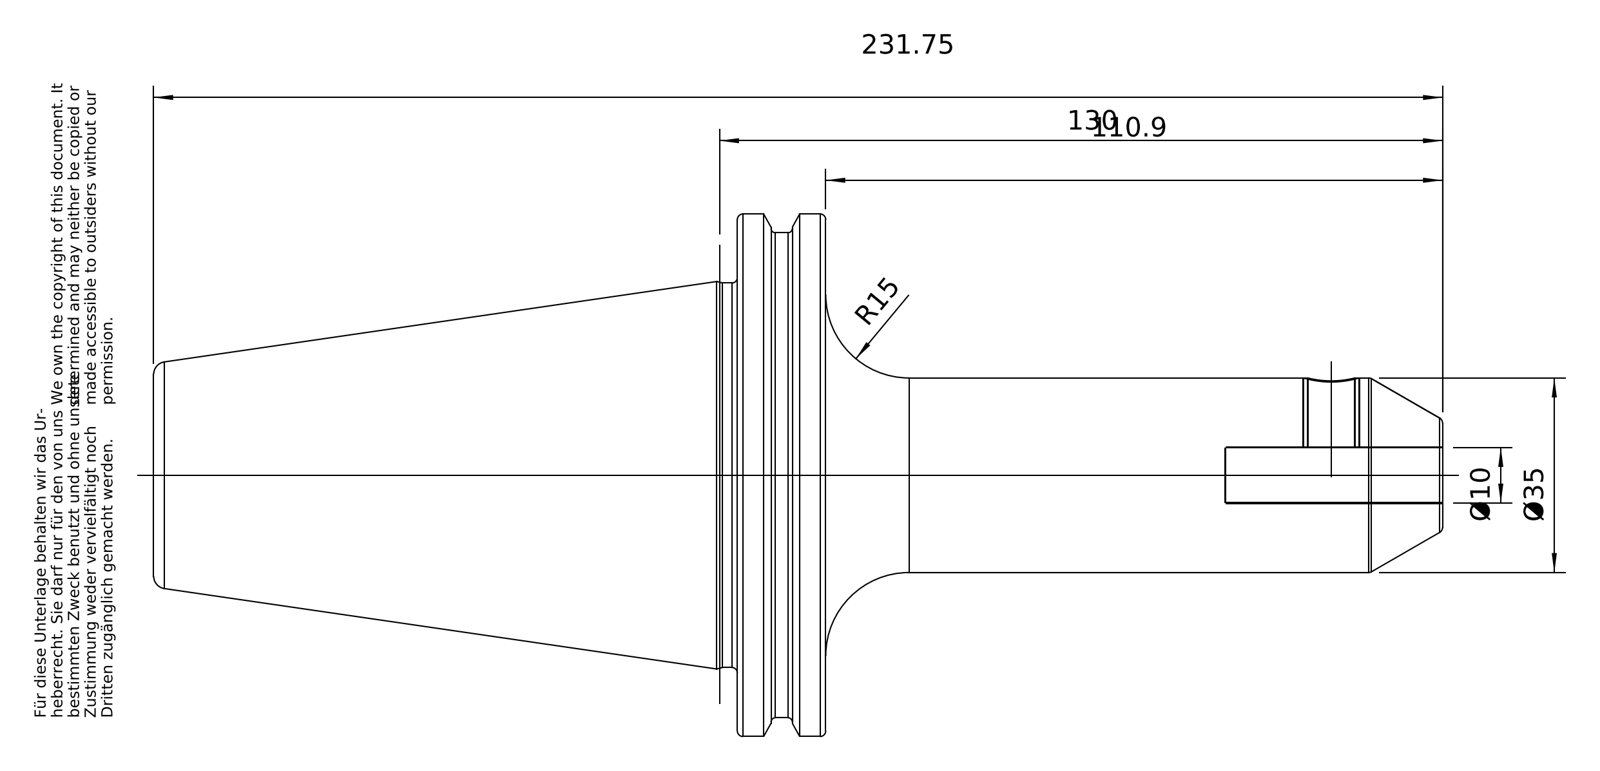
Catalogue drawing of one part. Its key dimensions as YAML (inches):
part_name: "50-304-10"
step_written_by: "PRO/ENGINEER BY PARAMETRIC TECHNOLOGY CORPORATION, 2010430 (CONFIG_CONTROL_DESIGN)"
units: inches
bodies: {solids: 1, faces: 103, planar: 21, cylindrical: 32, other: 50}
overall_size: [9.118, 3.837, 3.701]
volume: 27.1
surface_area: 85.72
round_holes:
  - {diameter: 0.394, count: 2}
  - {diameter: 0.335, count: 1}
  - {diameter: 0.817, count: 1}
  - {diameter: 0.985, count: 1}
  - {diameter: 1.012, count: 1}
round_bosses_or_shafts:
  - {diameter: 3.583, count: 1}
  - {diameter: 2.722, count: 1}
  - {diameter: 1.378, count: 1}
  - {diameter: 0.945, count: 1}
partial_cylinders:
  - {radius: 0.069, count: 5}
  - {radius: 1.919, count: 1}
face_to_face_distances: [0.624, 4.126, 4.75, 2.866, 1.016, 9.118, 4.992, 4.368, 1.89, 2.236]
